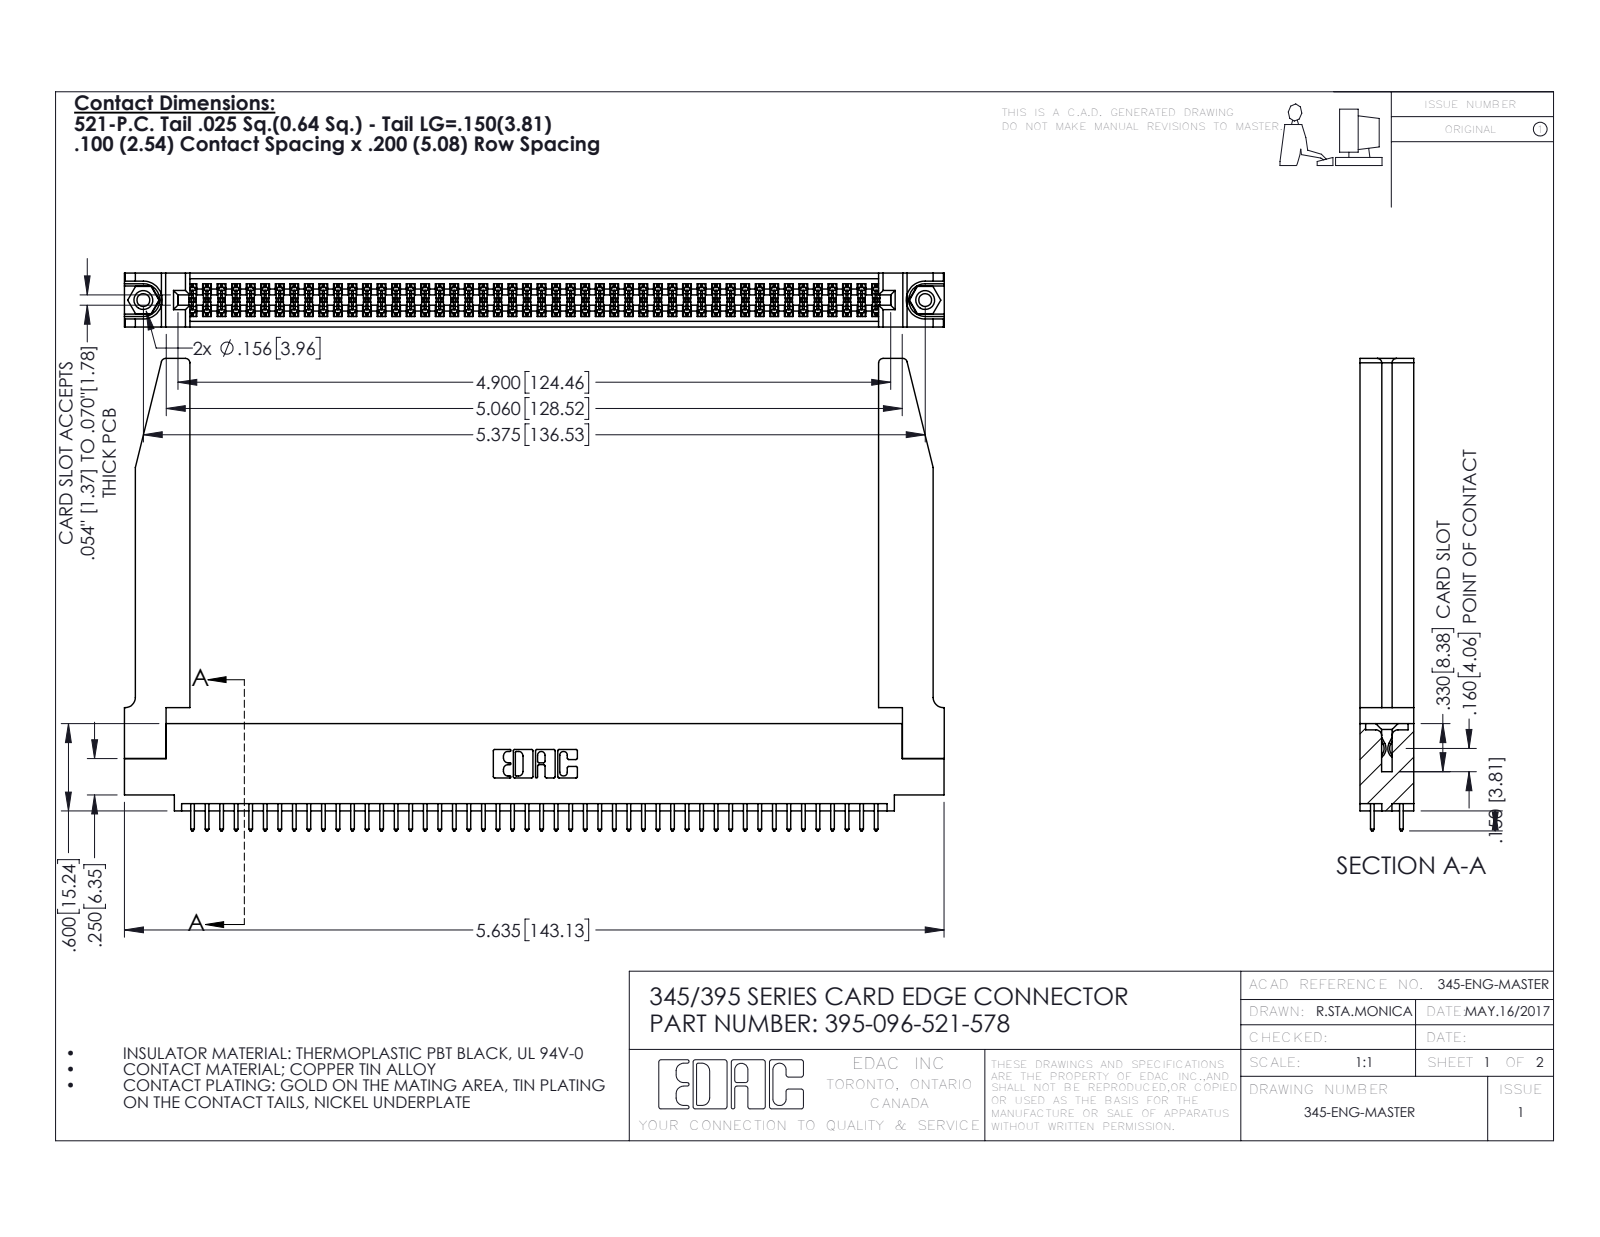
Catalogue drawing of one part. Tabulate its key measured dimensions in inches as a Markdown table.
| quantity | value |
| --- | --- |
| part name | 345-292-001_345-293-121; 395-096-521-578; 345-220-078_345-220-078; 345 Part_0.110 Offset - 0.156 Dia-TH (+1 more) |
| STEP written by | SolidWorks 2016 (CONFIG_CONTROL_DESIGN) |
| units | inches |
| bodies | 101 solids, 5164 faces (3394 planar, 1718 cylindrical, 52 other) |
| overall size | 5.636 × 3.247 × 0.37 |
| volume | 1.319 in³ |
| surface area | 42.26 in² |
| round holes (diameter × count) | 0.089 × 2, 0.125 × 2, 0.156 × 2, 0.064 × 1 |
| round bosses / shafts (diameter × count) | 0.155 × 2 |
| partial cylindrical surfaces (radius × count) | 0.006 × 144, 0.01 × 96, 0.01 × 22, 0.03 × 8, 0.007 × 6, 0.031 × 6, 0.026 × 3, 0.014 × 2 |
| main face-to-face distances | 0.072, 0.298, 0.37, 0.098, 0.272, 0.025, 0.2, 0.225, 0.175, 0.15 |
| hole center spacings | 0.27, 5.139, 5.375 |
